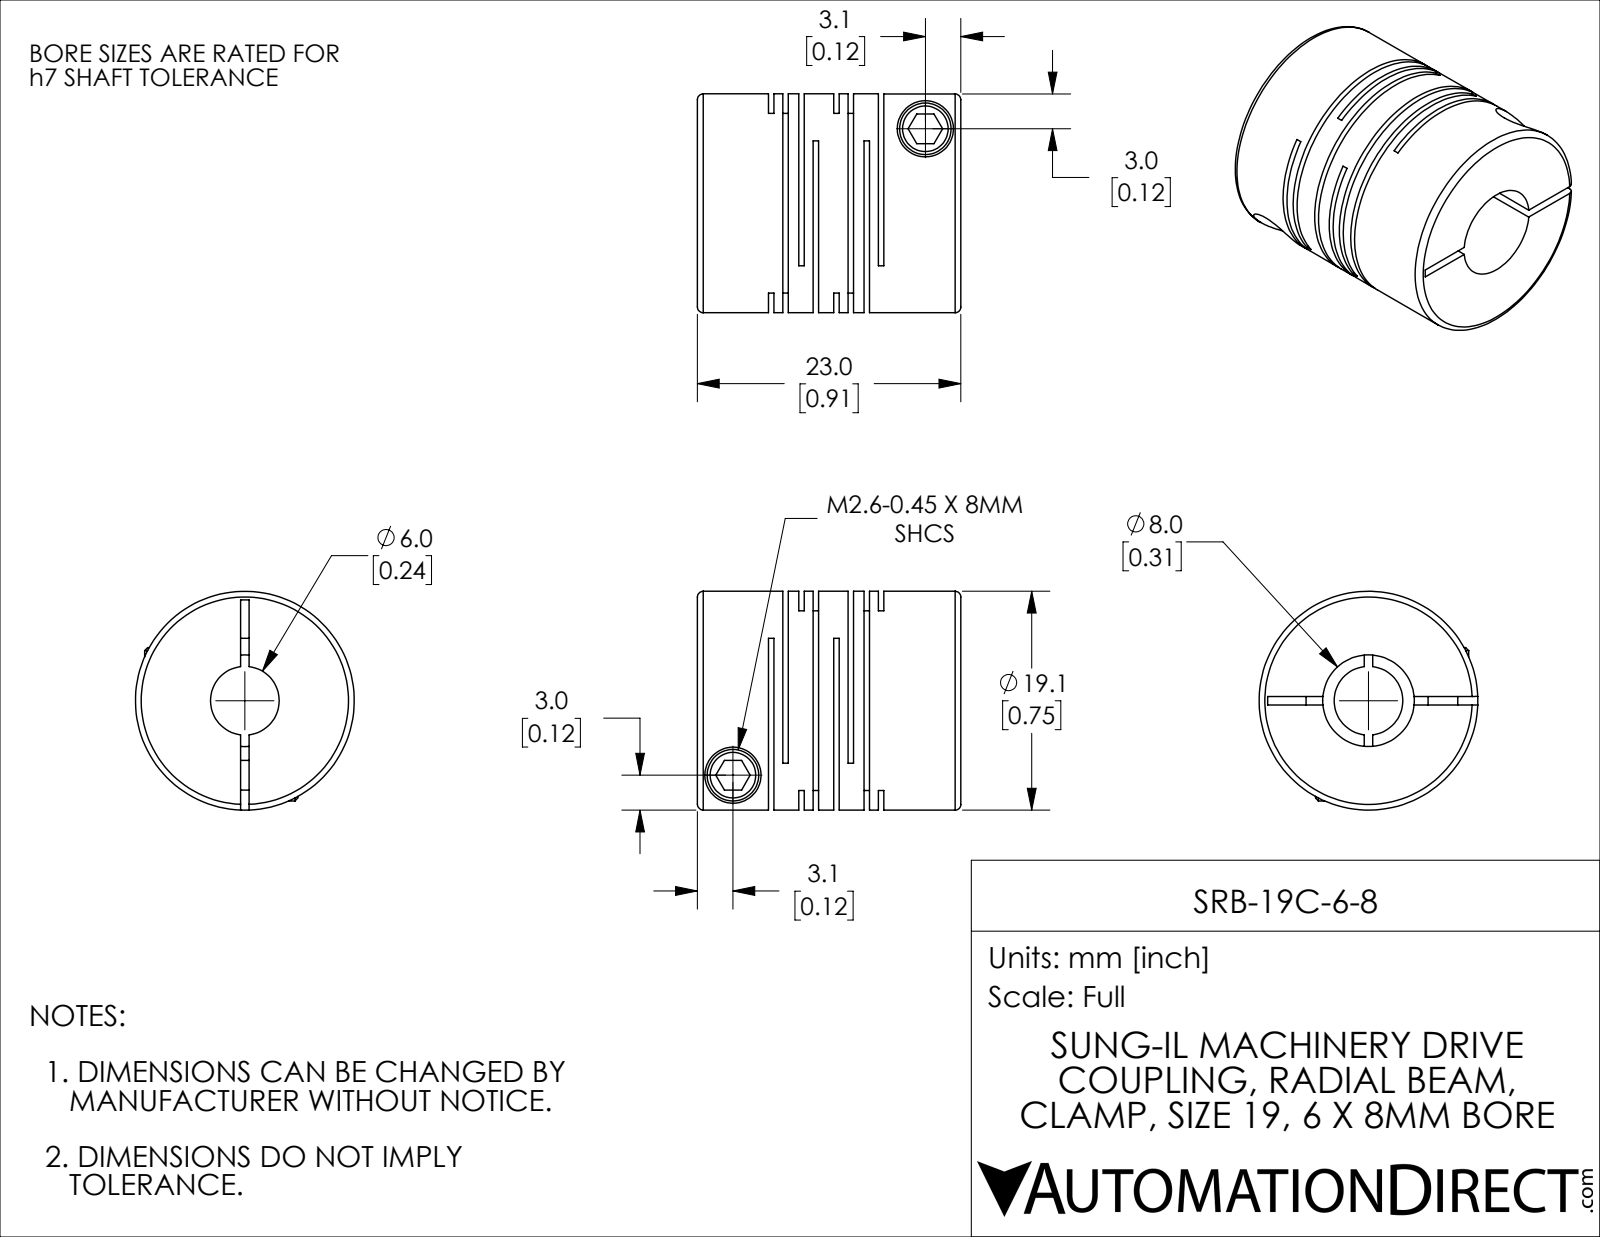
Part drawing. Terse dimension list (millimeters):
name: SRB-19C-6-8
written by: SolidWorks 2021 (CONFIG_CONTROL_DESIGN)
unit: mm
bodies: 1 solid, 114 faces (60 planar, 42 cylindrical, 12 other)
size: 23 × 19.1 × 19.1
volume: 4 606 mm³; area: 5 720 mm²
holes: 2× ⌀2.6, 2× ⌀4.9, 1× ⌀6, 1× ⌀8
bosses: 2× ⌀4.5, 1× ⌀19.1
face distances: 5.7, 0.48, 1.25, 2.65, 2.17, 3.05, 5.22, 4.45, 0.77, 1.4
